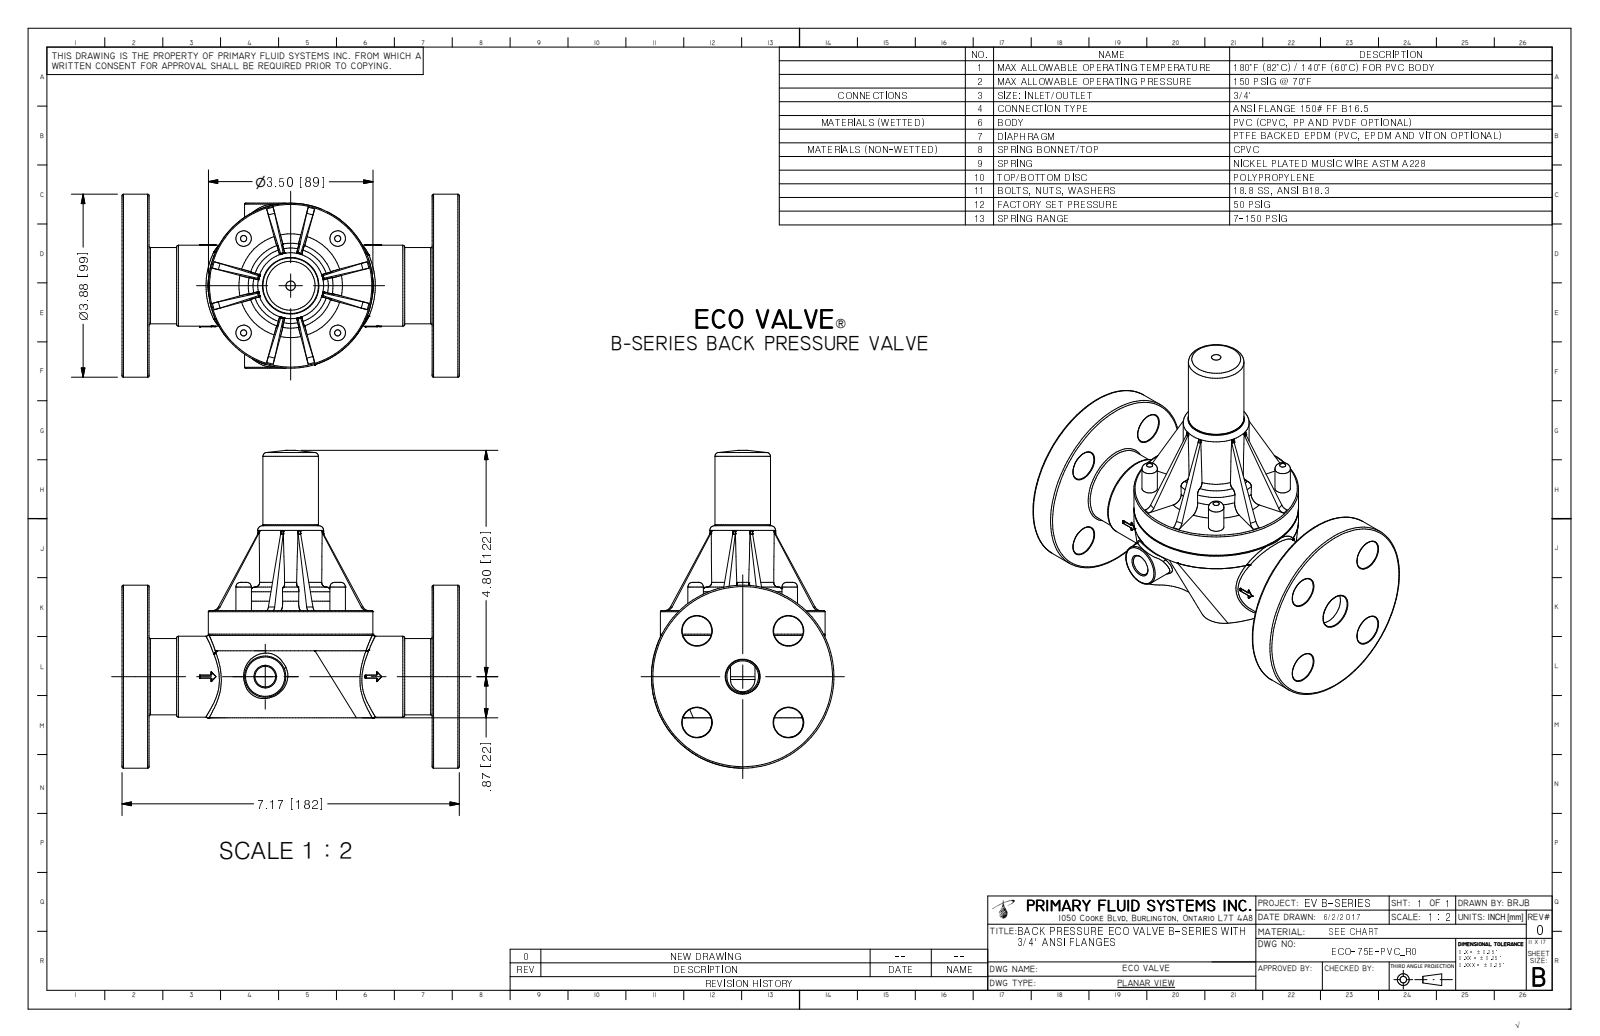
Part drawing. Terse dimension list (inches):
name: ECO-75E-PVC_R0
written by: Autodesk Inventor 2009 (AUTOMOTIVE_DESIGN)
unit: in
bodies: 1 solid, 358 faces (129 planar, 86 cylindrical, 143 other)
size: 7.17 × 6.741 × 3.88
volume: 40.9 in³; area: 180.4 in²
holes: 6× ⌀0.63, 4× ⌀0.23, 1× ⌀0.437, 1× ⌀0.722, 1× ⌀0.742
bosses: 4× ⌀0.33, 1× ⌀3.88, 1× ⌀3.5, 1× ⌀1.8, 1× ⌀1.716, 1× ⌀1.616, 1× ⌀1.4, 1× ⌀1.18
rounds: 8× R0.1, 8× R0.15, 4× R0.05, 1× R0.418, 1× R0.514, 1× R0.669, 1× R0.868, 1× R1.375
face distances: 7.17, 0.575, 6.594, 6.595, 6.02, 0.575, 2.275, 1.75, 0.525, 0.2
hole spacings: 1.944, 1.375, 2, 1.375, 1.945, 2.75, 2.75, 2.828
